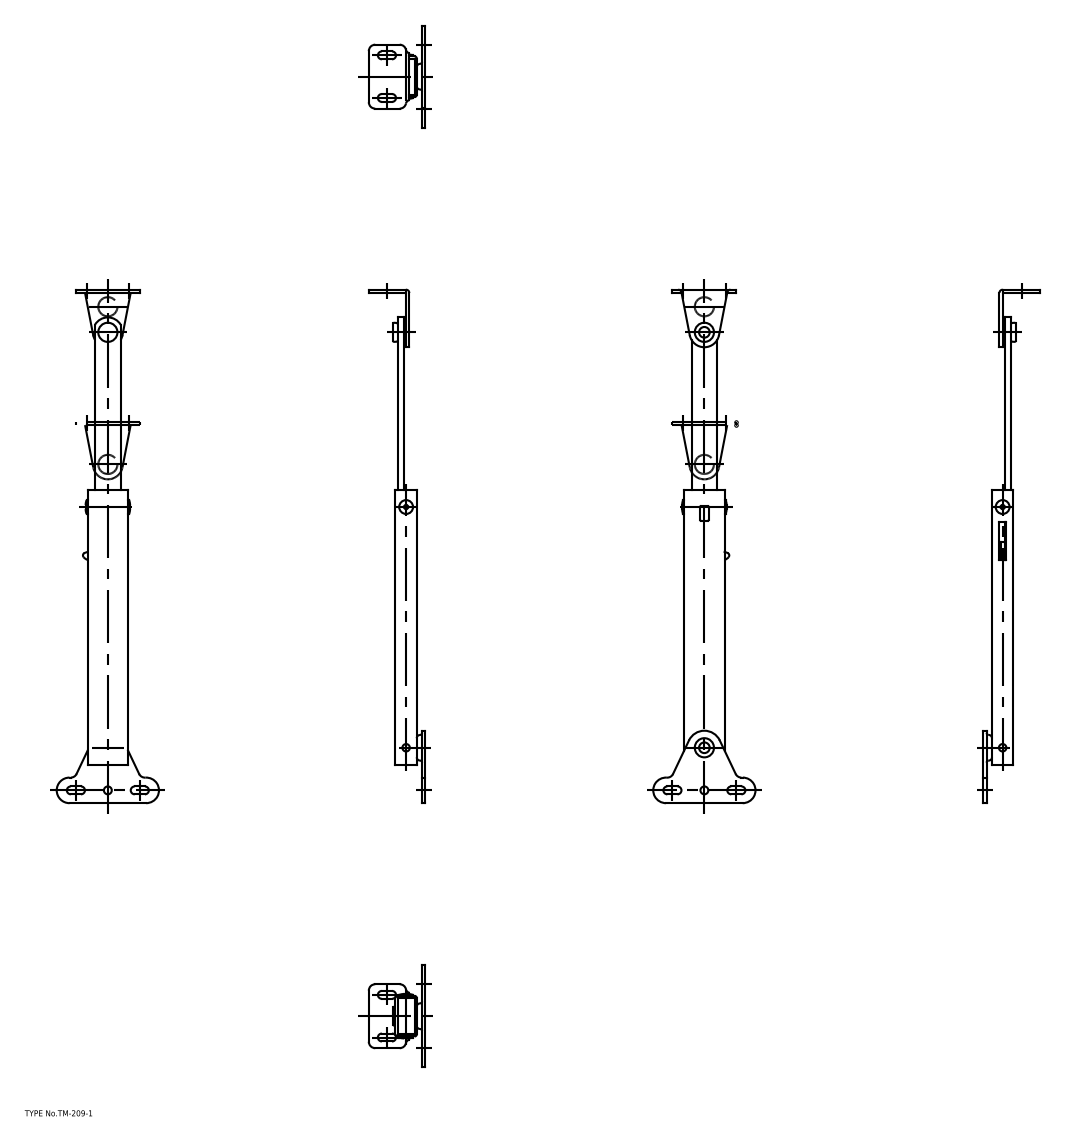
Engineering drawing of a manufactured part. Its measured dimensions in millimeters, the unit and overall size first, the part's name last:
Units: millimetres
Overall size (bounding box): 241 × 48 × 26.5
Round holes (diameter × count): ⌀5 ×2, ⌀2 ×1, ⌀3.5 ×1, ⌀3.7 ×1, ⌀4 ×1, ⌀9 ×1
Round bosses / shafts (diameter × count): ⌀6 ×2, ⌀11 ×1, ⌀6.5 ×1
Partial cylindrical surfaces — rounded edges, fillets, slot ends (radius × count): R0.5 ×11, R1 ×8, R3 ×6, R4.25 ×4, R1.5 ×3, R6 ×2, R1.25 ×1, R4 ×1
Main face-to-face distances: 1, 9, 4, 5, 10, 8, 2.5, 3.5, 18, 6
Hole centre spacings: 20, 113, 195, 215
Volume: 16 566 mm³ · Surface area: 24 862 mm²
Bodies: 11 solids, 214 faces (107 planar, 85 cylindrical, 22 other)
Part name (STEP PRODUCT): bracket_B; bracket_A; rivet_3; rotor (+5 more)
STEP written by: spGate 19.8.4 (****-****-****-****) (AUTOMOTIVE_DESIGN)
